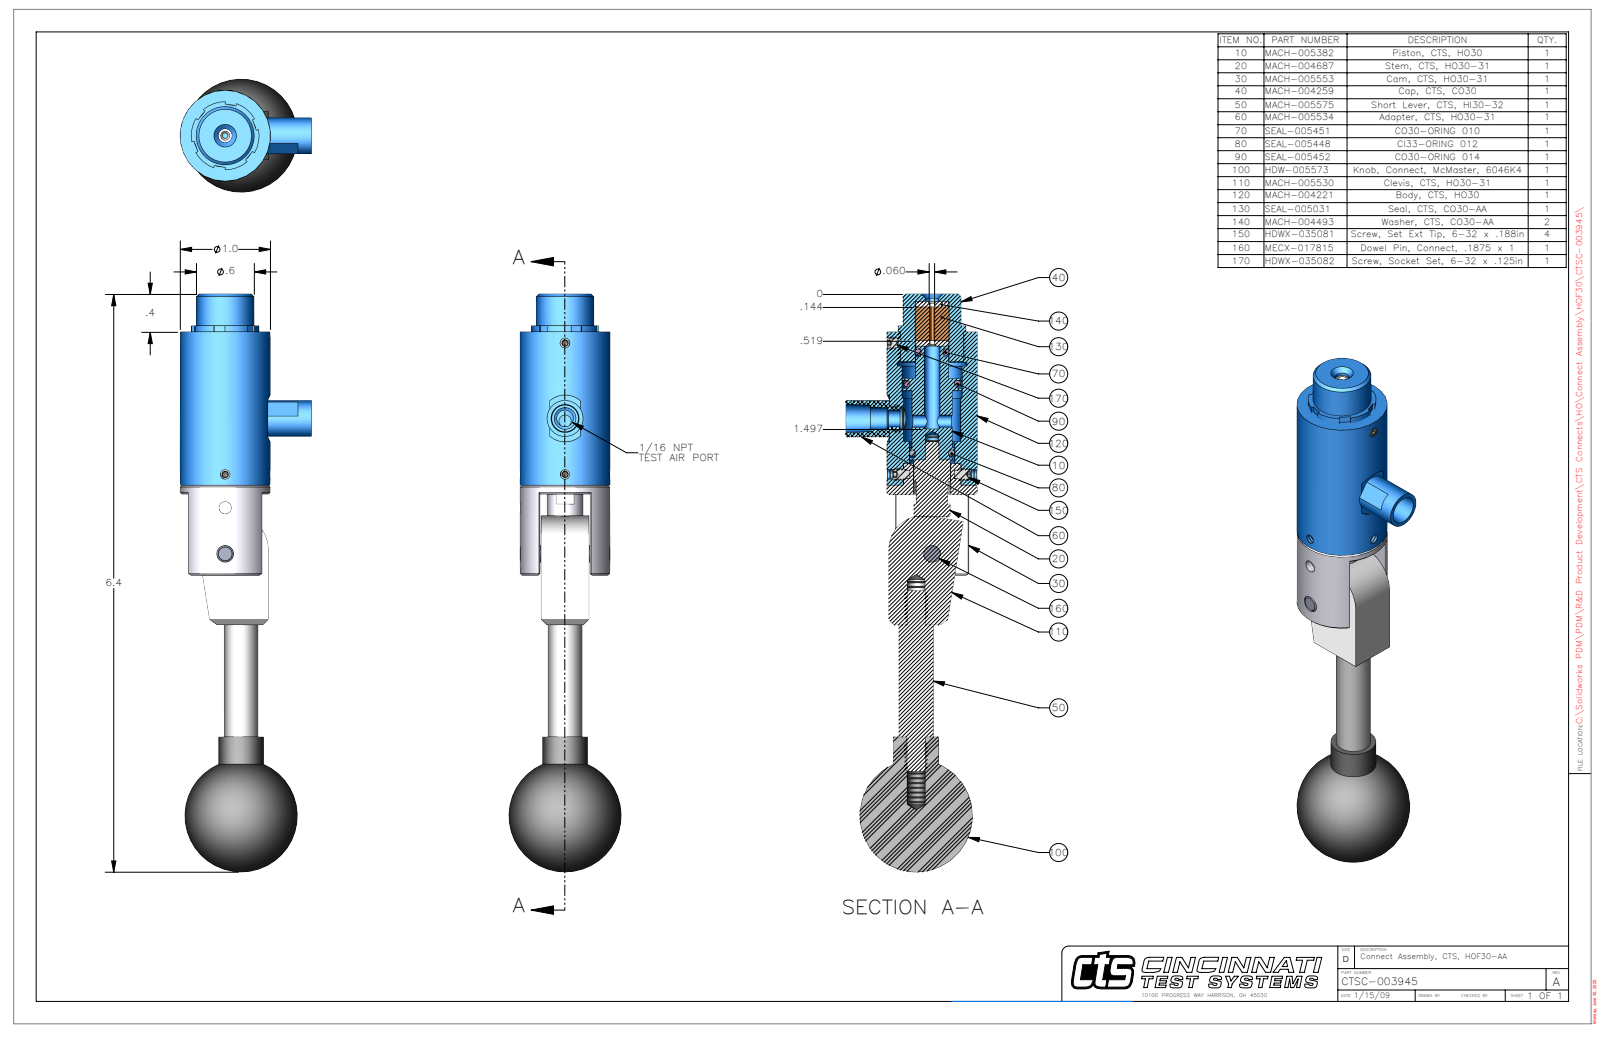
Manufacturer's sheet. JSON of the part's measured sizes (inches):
{"part_name": "CTSC-003945", "step_written_by": "SolidWorks 2023 (AUTOMOTIVE_DESIGN)", "units": "inches", "bodies": {"solids": 13, "faces": 460, "planar": 168, "cylindrical": 161, "other": 131}, "overall_size": [6.407, 1.455, 1.25], "volume_in3": 3.403, "surface_area_in2": 32.69, "round_holes": [[0.107, 3], [0.06, 1], [0.062, 1], [0.136, 1], [0.138, 1], [0.15, 1], [0.15, 1], [0.175, 1], [0.187, 1], [0.189, 1], [0.19, 1], [0.201, 1]], "round_bosses_or_shafts": [[0.138, 3], [0.4, 2], [0.092, 2], [1, 1], [0.642, 1], [0.63, 1], [0.5, 1], [0.49, 1]], "partial_cylinders_radius": [[0.26, 1], [0.349, 1], [0.374, 1], [0.375, 1]], "face_to_face_distances": [0.012, 0.542, 0.53, 0.554, 1.8, 0.059, 0.434, 1.447, 3.247, 1.24], "hole_center_spacings": [0.03, 0.176, 0.37, 0.51, 0.59, 0.62, 0.835, 0.865]}
